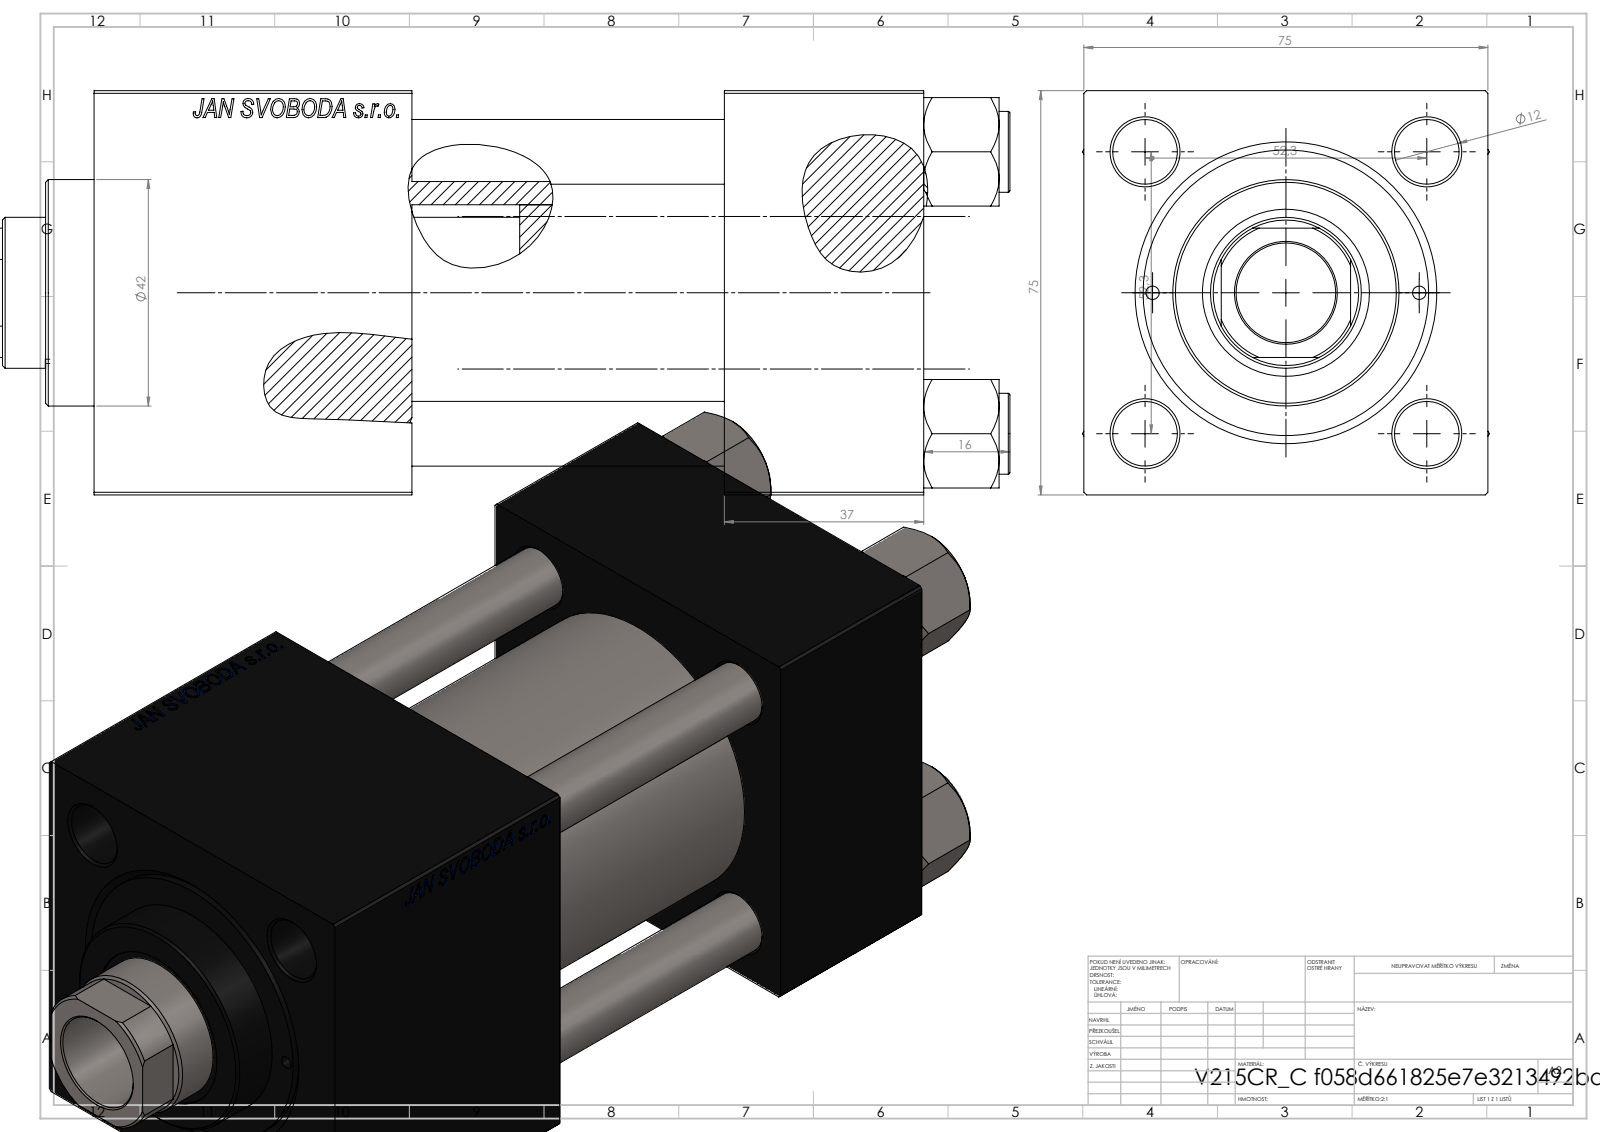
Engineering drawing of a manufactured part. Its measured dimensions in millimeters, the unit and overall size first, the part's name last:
Units: millimetres
Overall size (bounding box): 195 × 75.54 × 75
Round holes (diameter × count): ⌀12 ×4, ⌀2.5 ×2, ⌀7 ×2, ⌀20.96 ×2, ⌀30 ×2, ⌀18.5 ×1, ⌀28 ×1, ⌀31 ×1, ⌀41 ×1, ⌀50 ×1, ⌀53 ×1
Round bosses / shafts (diameter × count): ⌀15 ×4, ⌀56 ×1, ⌀42 ×1
Partial cylindrical surfaces — rounded edges, fillets, slot ends (radius × count): R13.5 ×1
Main face-to-face distances: 75, 37, 154, 117, 95, 58, 59, 125.3, 88.3, 30.3
Hole centre spacings: 26.19, 36.98, 52.3, 57.22, 24.75, 73.96, 49.5, 93.5
Volume: 668 945 mm³ · Surface area: 151 012 mm²
Bodies: 11 solids, 1155 faces (528 planar, 91 cylindrical, 536 other)
Part name (STEP PRODUCT): V215CR_C_Body; V215CR_C_TYCINKA; V215_VC_A; V215CR_VCP_C (+1 more)
STEP written by: SolidWorks 2019 (CONFIG_CONTROL_DESIGN)
